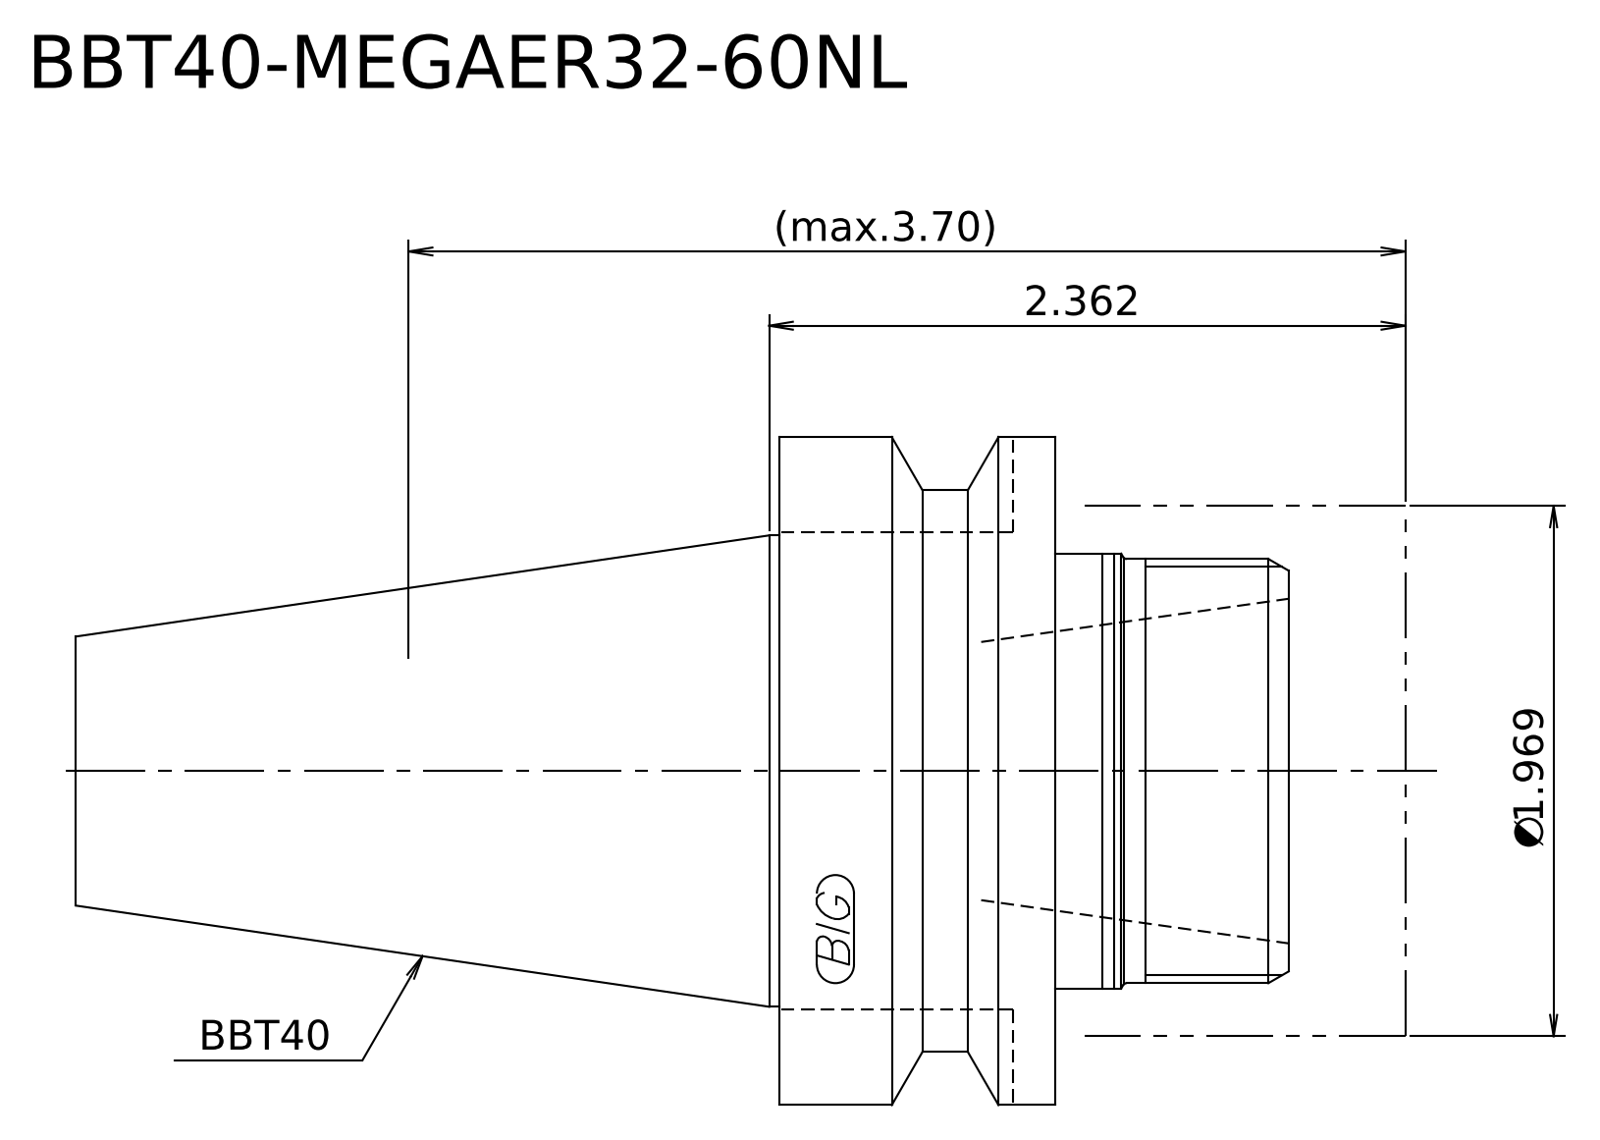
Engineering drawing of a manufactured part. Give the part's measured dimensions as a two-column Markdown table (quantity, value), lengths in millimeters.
| quantity | value |
| --- | --- |
| STEP written by | Kubotek KeyCreator 2011 V10.0.2 (22737) (automotive_design) |
| units | millimeters |
| bodies | 2 solids, 18 faces (6 planar, 7 cylindrical, 5 other) |
| overall size | 125.4 × 63 × 63 |
| volume | 227 365 mm³ |
| surface area | 29 873 mm² |
| round bosses / shafts (diameter × count) | 63 × 1, 53 × 1, 50 × 1, 44.45 × 1, 41 × 1, 40 × 1 |
| main face-to-face distances | 30.2, 33, 2.8, 59, 28.8, 26, 11, 19.2, 22, 48 |
